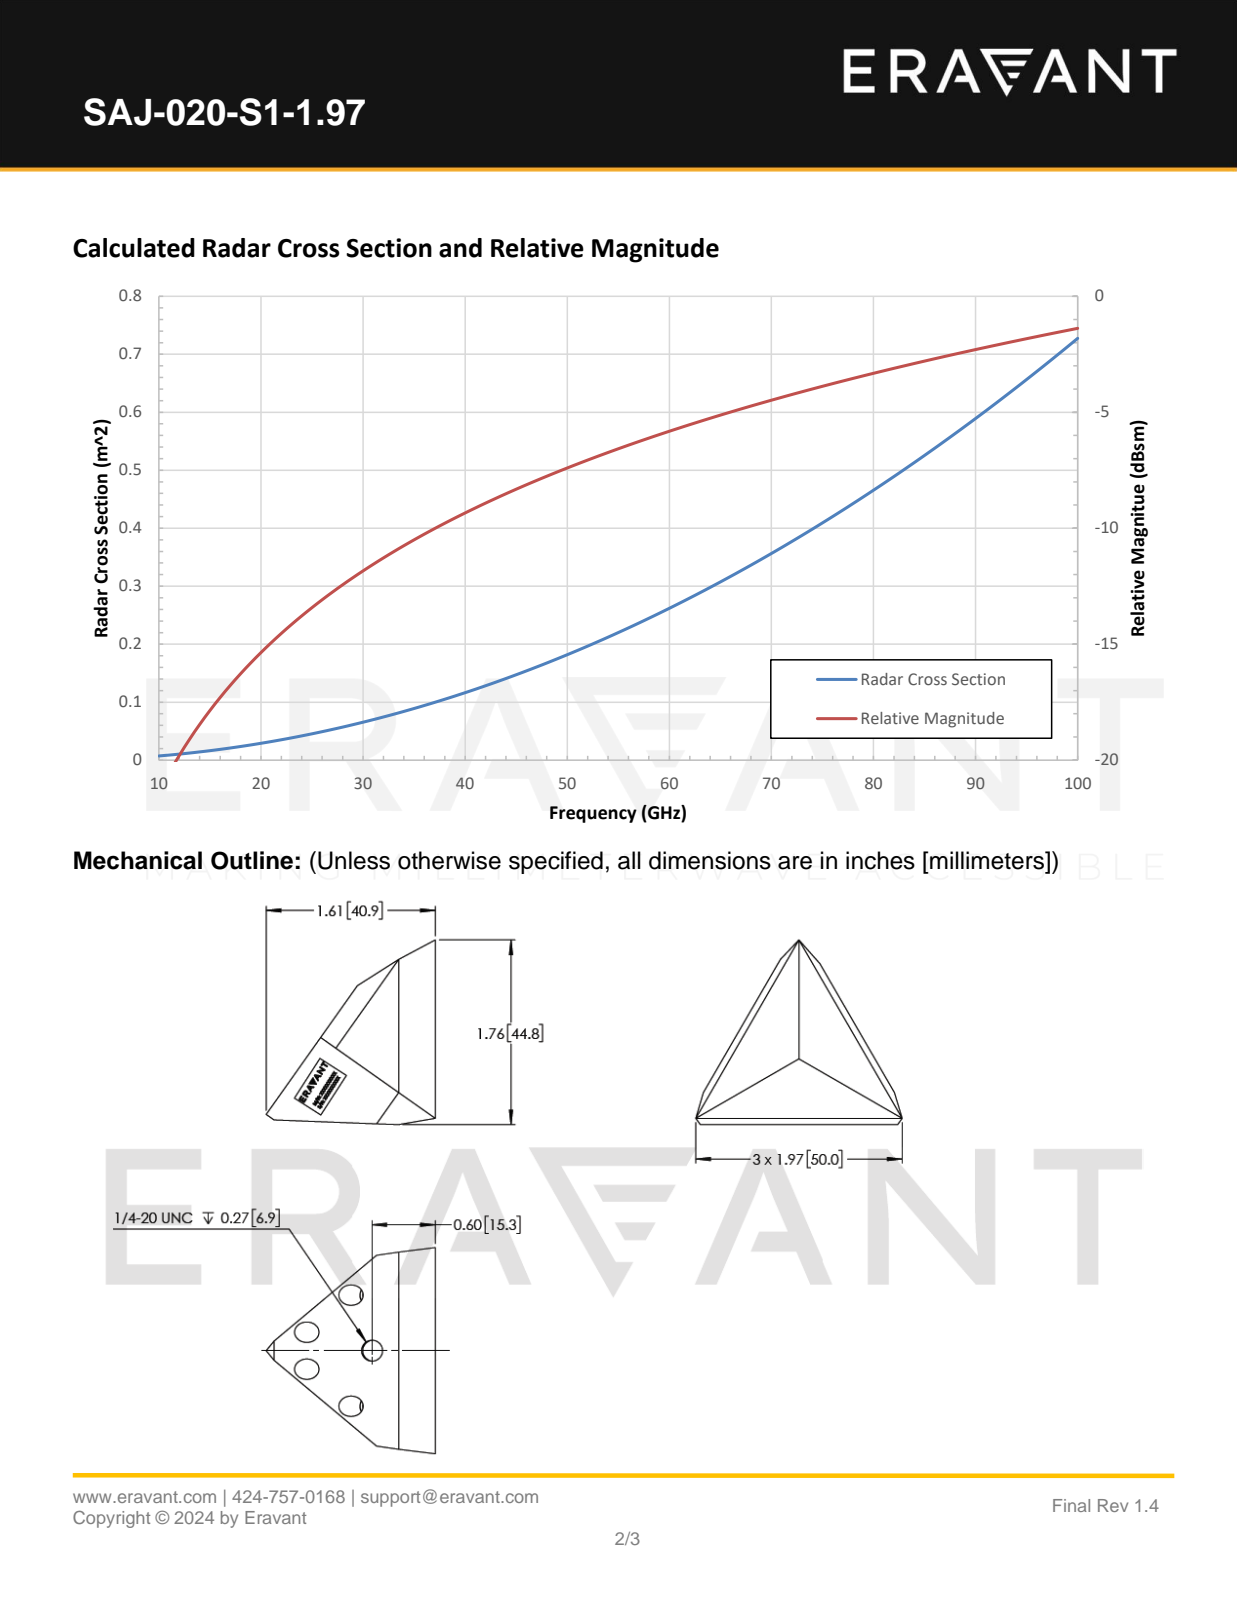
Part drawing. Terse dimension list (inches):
name: SAJ-020-S1-1.97
written by: SolidWorks 2020 (CONFIG_CONTROL_DESIGN)
unit: in
bodies: 8 solids, 458 faces (74 planar, 297 cylindrical, 87 other)
size: 2.292 × 1.969 × 1.338
volume: 0.997 in³; area: 15.01 in²
holes: 5× ⌀0.089, 5× ⌀0.129, 5× ⌀0.195, 1× ⌀0.201
bosses: 5× ⌀0.183, 5× ⌀0.112, 5× ⌀0.08
face distances: 0.25, 0.25, 0.12, 0.112, 0.232, 0.094, 0.042, 0.07, 0.138, 0.138
hole spacings: 0.5, 0.791, 0.354, 1.061
